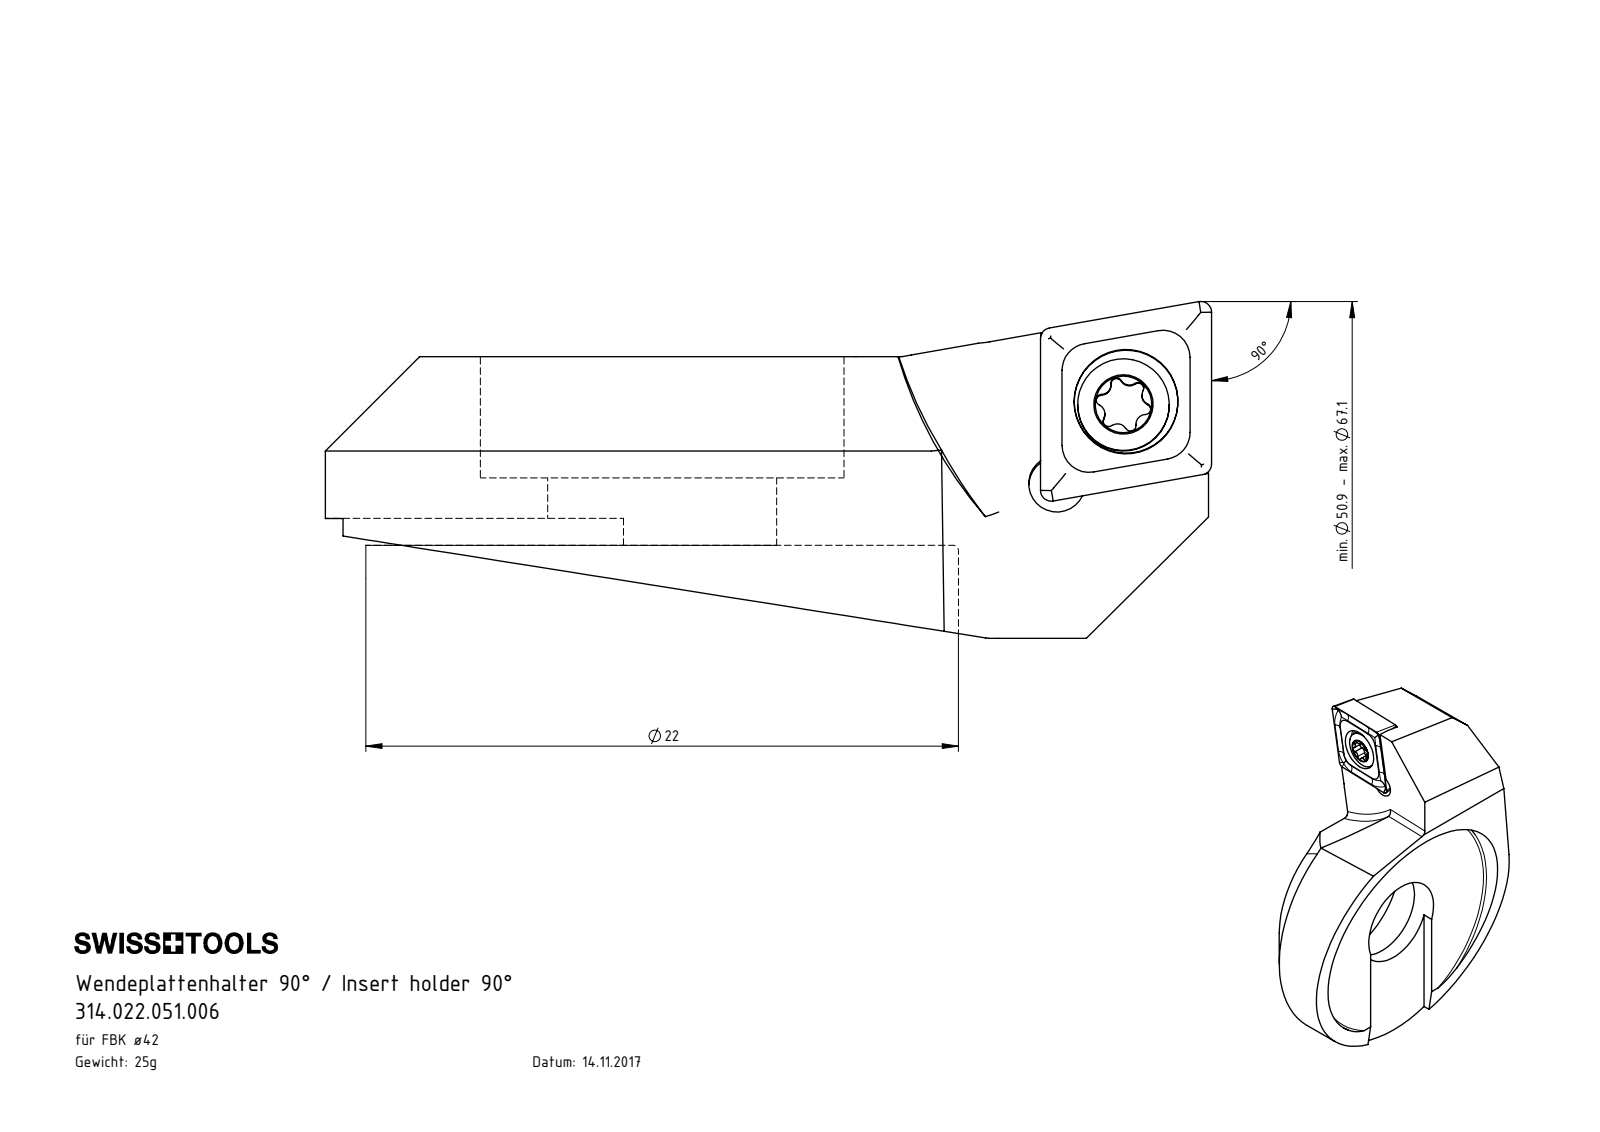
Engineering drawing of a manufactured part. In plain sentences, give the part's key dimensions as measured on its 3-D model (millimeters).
The part is named "CCMT060204; F42-WCA.001.009_C_fertigbearbeitet; WCA-ER2.001.006_A; F42.WCA.001.009". Its 3-D file was written by "SolidWorks 2017 (AUTOMOTIVE_DESIGN)". It is 3 solids with 103 faces: 39 planar, 26 cylindrical and 38 other. Overall it measures 32.9 by 25 by 12.5 millimeters. Its volume is 3 141 cubic millimeters and its surface area 2 312 square millimeters. Round holes: 1 of diameter 2.05, 1 of diameter 2.1, 1 of diameter 2.8, 1 of diameter 3.85, 1 of diameter 8.5, 1 of diameter 13.5. Round bosses or shafts: 1 of diameter 3.4, 1 of diameter 2.5. Partial cylindrical surfaces (rounded edges, fillets, slot ends): 6 of radius 0.21, 5 of radius 0.36, 2 of radius 0.5, 1 of radius 0.36, 1 of radius 5, 1 of radius 11, 1 of radius 12.5, 1 of radius 16. The main face-to-face distances are 7, 4.5, 2.5, 6, 1.5, 1, 2.28, 10.45, 5.95, 4.45. The hole center spacings are 3.84, 3.99.
